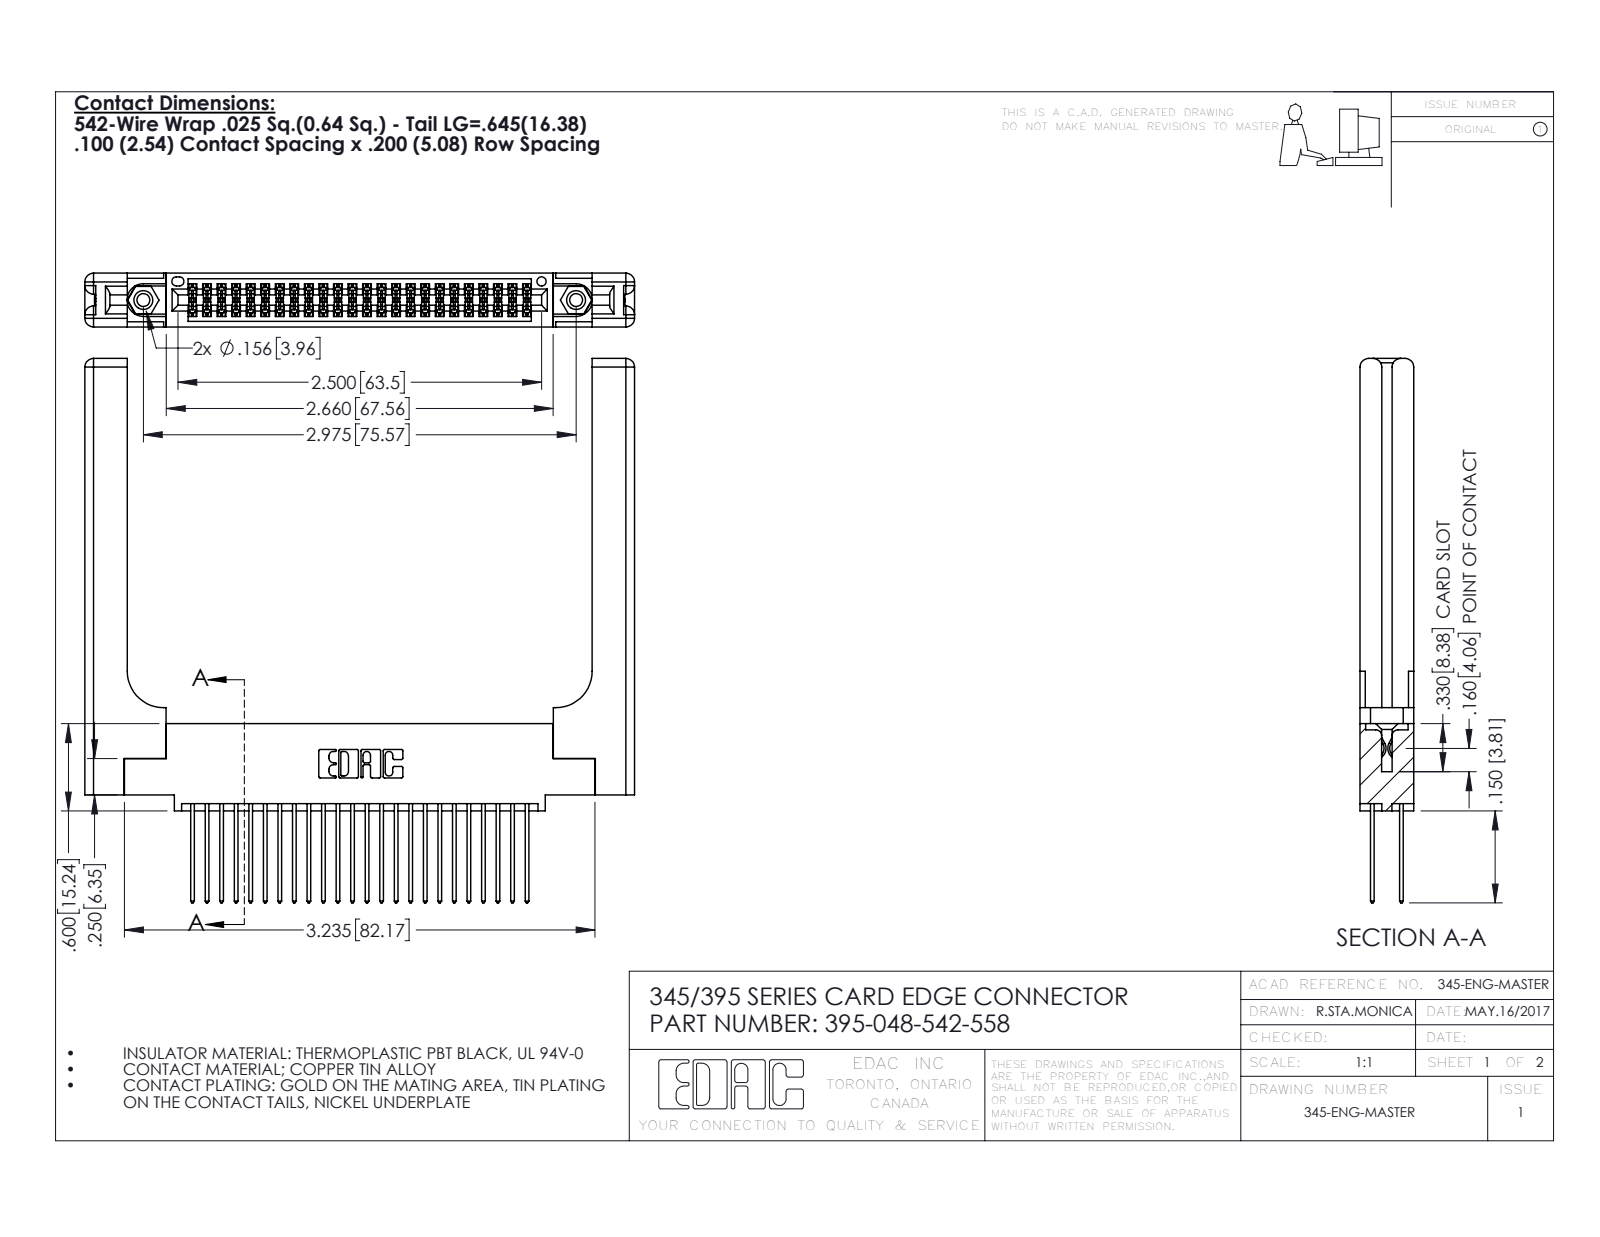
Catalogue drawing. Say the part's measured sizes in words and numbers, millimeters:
The part is named "345 Part_0.110 Offset - 0.156 Dia-TH; 395-048-542-558; 345-250-001_345-250-001-102; 345-292-001_345-293-142 (+1 more)". Its 3-D file was written by "SolidWorks 2016 (CONFIG_CONTROL_DESIGN)". It is 53 solids with 2786 faces: 1816 planar, 910 cylindrical and 60 other. Overall it measures 96 by 95 by 9.4 millimeters. Its volume is 17 780 cubic millimeters and its surface area 19 610 square millimeters. Round holes: 2 of diameter 2.3, 2 of diameter 3.2, 2 of diameter 4, 1 of diameter 1.6. Round bosses or shafts: 2 of diameter 3.9. Partial cylindrical surfaces (rounded edges, fillets, slot ends): 72 of radius 0.2, 48 of radius 0.3, 22 of radius 0.3, 16 of radius 1.5, 6 of radius 0.2, 6 of radius 0.8, 3 of radius 0.7, 2 of radius 0.4. The main face-to-face distances are 1.8, 9.4, 7.6, 2.5, 6.9, 0.6, 5.1, 5.7, 3.8, 3.8. The hole center spacings are 6.9, 69.6, 75.6.
